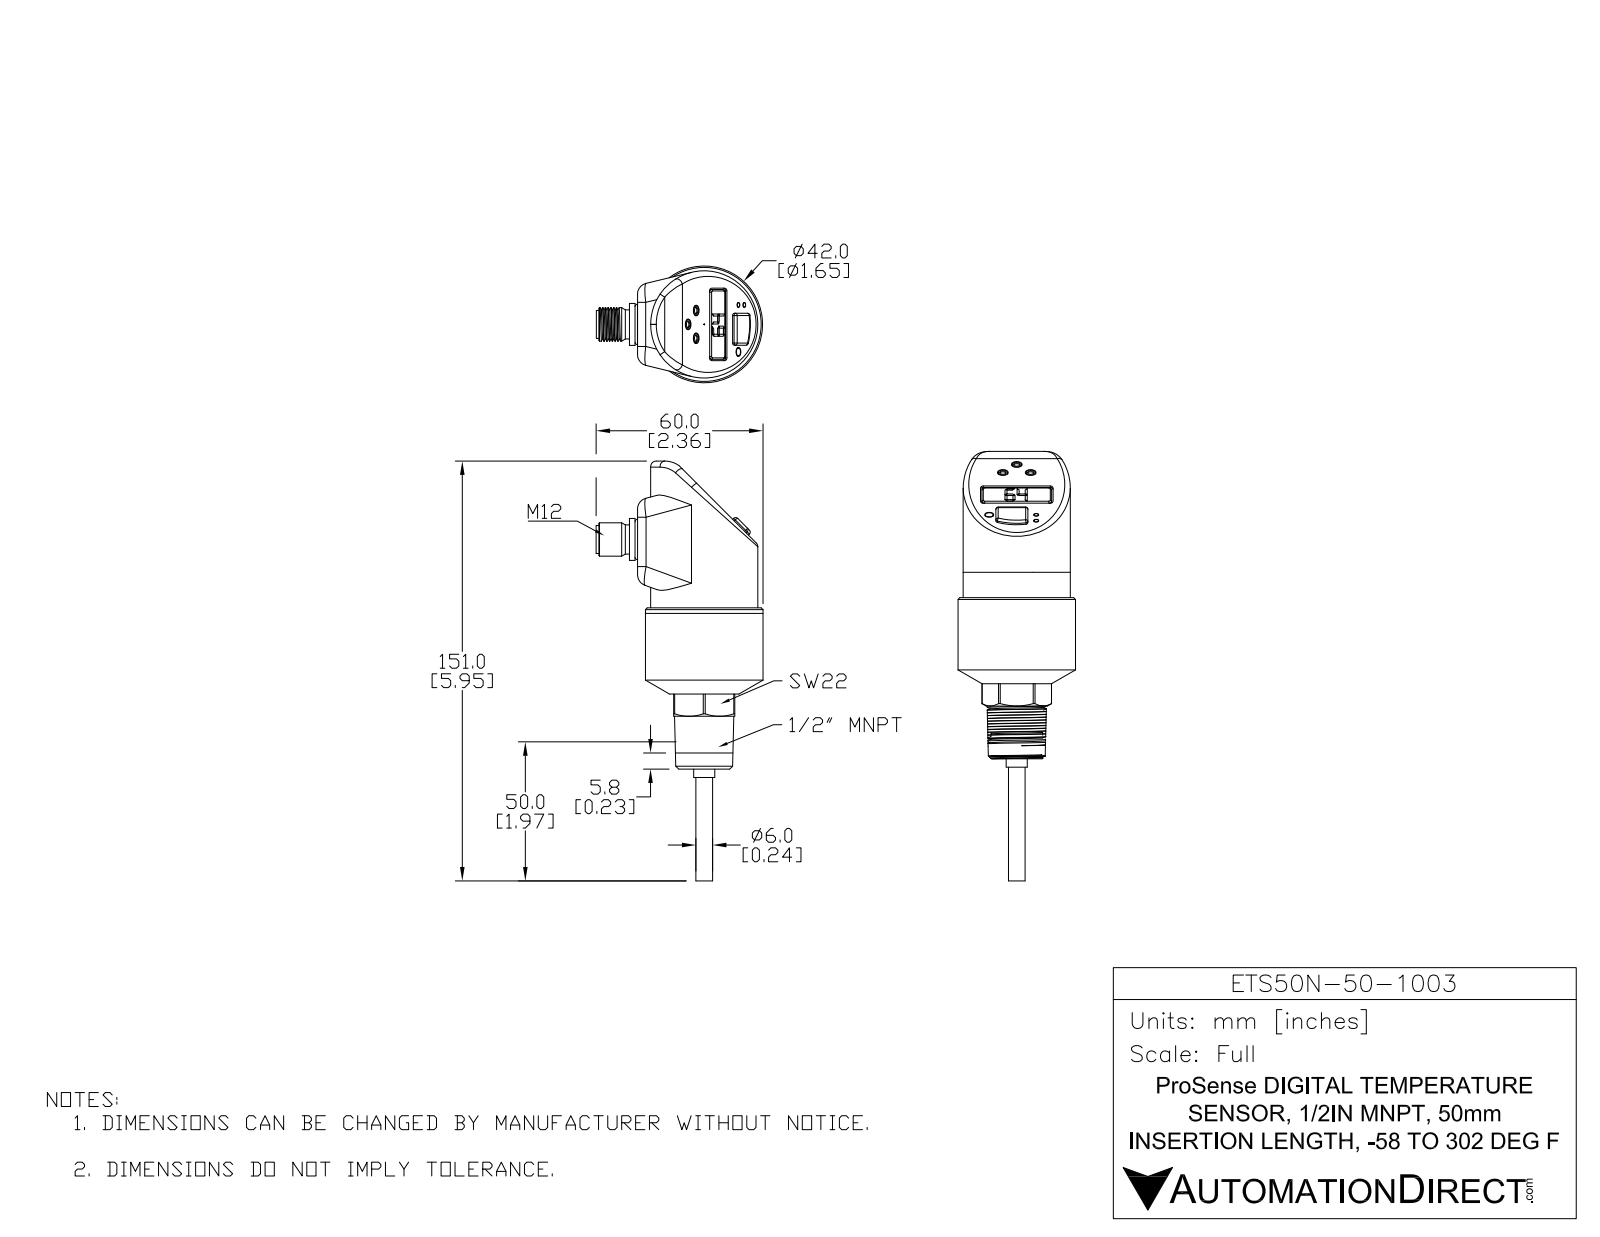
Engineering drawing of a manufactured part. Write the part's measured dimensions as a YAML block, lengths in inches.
part_name: "ETS50N-50-1003"
step_written_by: "SolidWorks 2016 (AUTOMOTIVE_DESIGN)"
units: inches
bodies: {solids: 1, faces: 324, planar: 138, cylindrical: 95, other: 91}
overall_size: [6.082, 2.36, 1.665]
volume: 6.575
surface_area: 29.01
round_holes:
  - {diameter: 0.333, count: 1}
  - {diameter: 0.433, count: 1}
round_bosses_or_shafts:
  - {diameter: 0.055, count: 4}
  - {diameter: 0.039, count: 4}
  - {diameter: 1.665, count: 1}
  - {diameter: 1.518, count: 1}
  - {diameter: 0.594, count: 1}
  - {diameter: 0.573, count: 1}
  - {diameter: 0.472, count: 1}
  - {diameter: 0.413, count: 1}
partial_cylinders:
  - {radius: 0.039, count: 8}
  - {radius: 0.031, count: 7}
  - {radius: 0.02, count: 4}
  - {radius: 0.157, count: 4}
  - {radius: 0.276, count: 4}
  - {radius: 0.024, count: 1}
  - {radius: 0.079, count: 1}
  - {radius: 0.355, count: 1}
face_to_face_distances: [0.866, 2.283, 0.547, 0.512, 0.035, 0.079, 0.114, 0.626, 1.492, 1.378]
